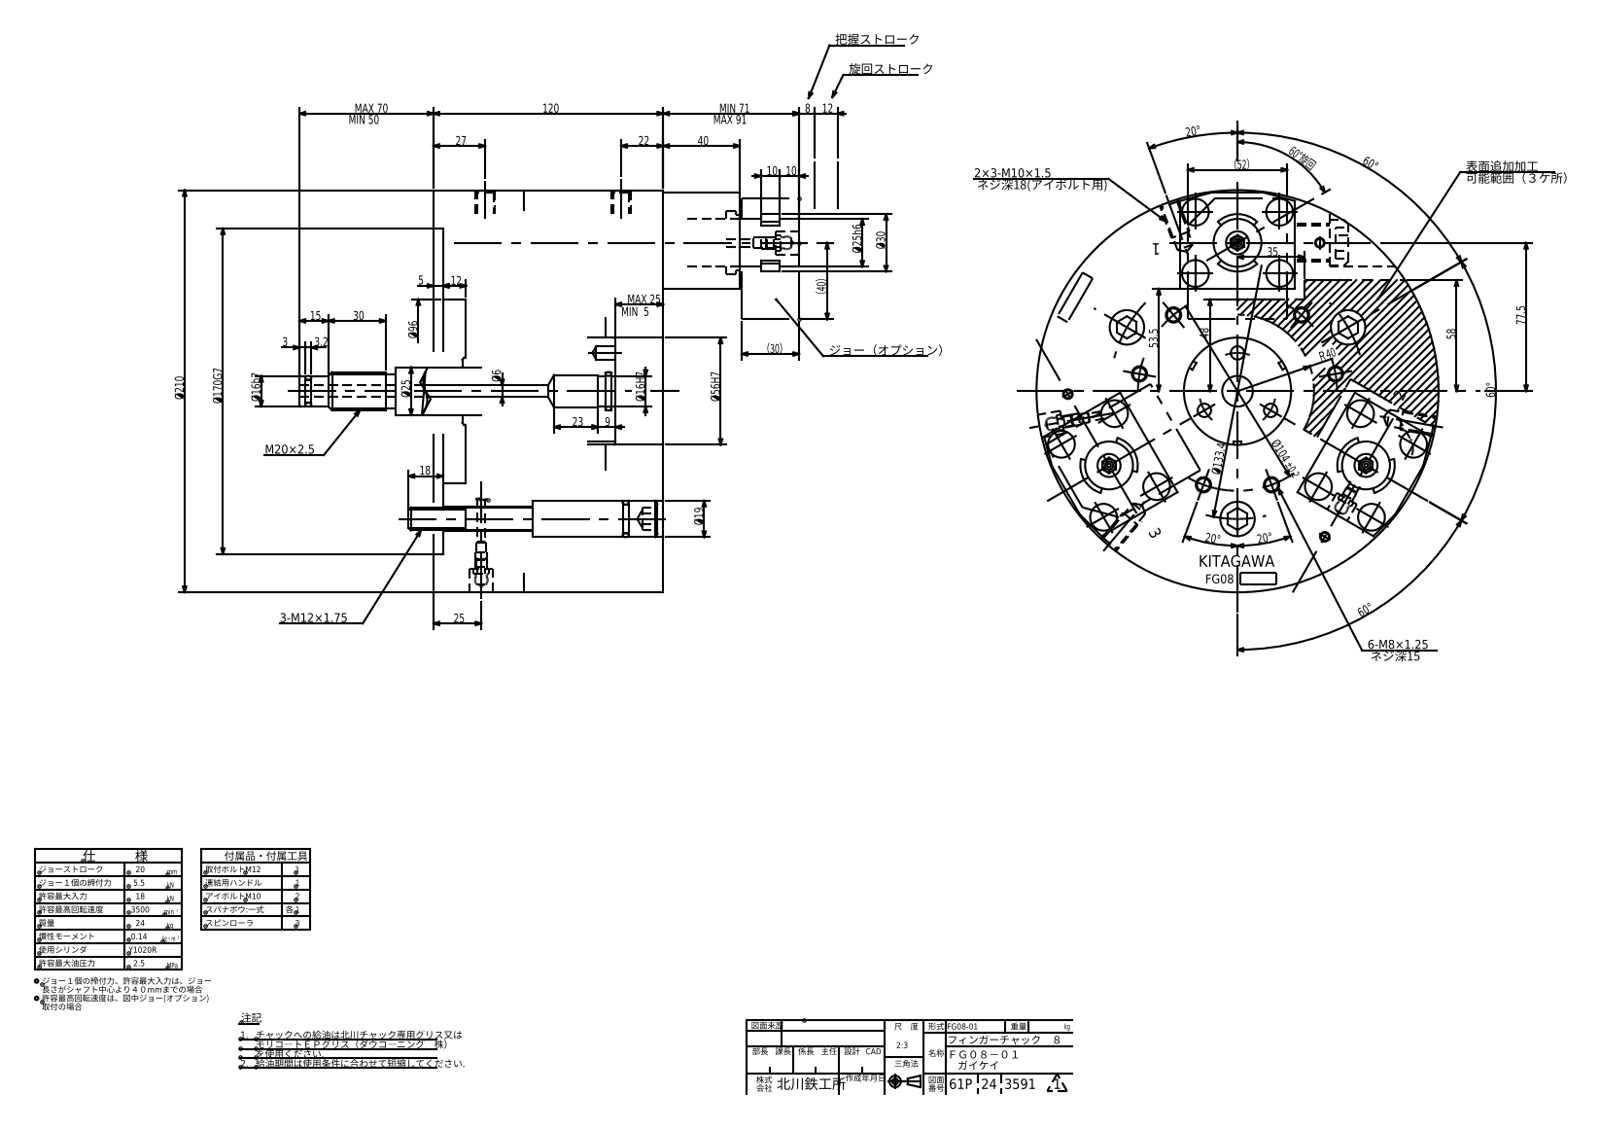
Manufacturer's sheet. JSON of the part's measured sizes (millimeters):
{"part_name": "FG08_mid stroke", "step_written_by": "ST-DEVELOPER v16.7 (AUTOMOTIVE_DESIGN)", "units": "millimeters", "bodies": {"solids": 46, "faces": 1093, "planar": 545, "cylindrical": 324, "other": 224}, "overall_size": [261, 210.31, 210], "volume_mm3": 3713000, "surface_area_mm2": 619610, "round_holes": [[6.8, 18], [9, 12], [14, 12], [5, 6], [15, 6], [17, 6], [16, 4], [30, 4], [35, 4], [3, 3], [4, 3], [5.2, 3]], "round_bosses_or_shafts": [[13, 12], [7.76, 12], [10, 6], [24, 4], [12, 4], [20, 3], [19, 3], [18, 3]], "partial_cylinders_radius": [[1.5, 24], [10, 6], [11, 3], [12.3, 3], [12.5, 3], [95, 1], [97, 1]], "face_to_face_distances": [30, 43, 47, 60, 5, 73, 13, 15, 152, 17], "hole_center_spacings": [27.2, 25.19, 27.5, 32, 44, 50.36, 62.58, 69.98]}
